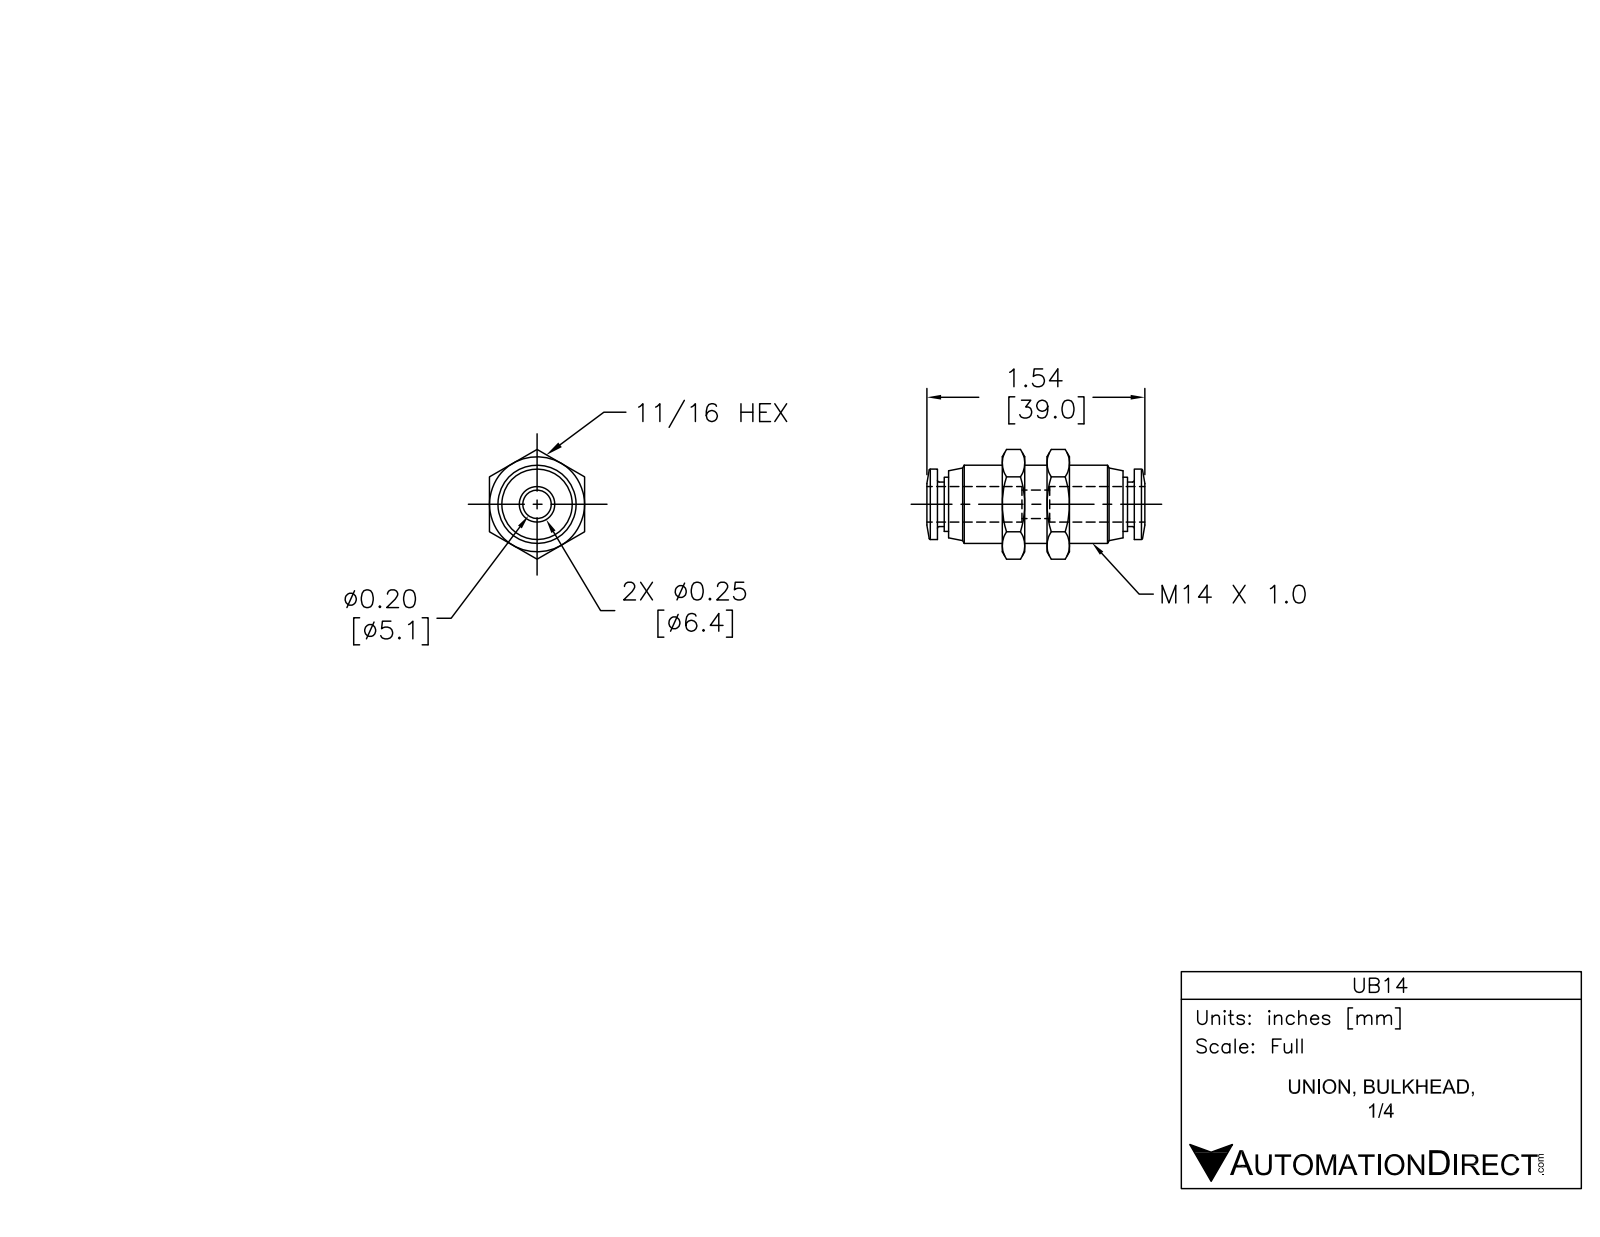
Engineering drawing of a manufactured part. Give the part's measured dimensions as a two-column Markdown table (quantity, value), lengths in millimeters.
| quantity | value |
| --- | --- |
| part name | UB14 |
| STEP written by | SolidWorks 2015 (AUTOMOTIVE_DESIGN) |
| units | millimeters |
| bodies | 1 solid, 104 faces (24 planar, 24 cylindrical, 56 other) |
| overall size | 39 × 19.6 × 17 |
| volume | 4 820 mm³ |
| surface area | 3 304 mm² |
| round holes (diameter × count) | 5 × 1, 6.6 × 1 |
| round bosses / shafts (diameter × count) | 14 × 1, 12.6 × 1, 9.7 × 1, 8 × 1 |
| main face-to-face distances | 4, 17, 8, 11.6, 15.6, 19.6, 23.6, 2, 33.2, 9.6 |
